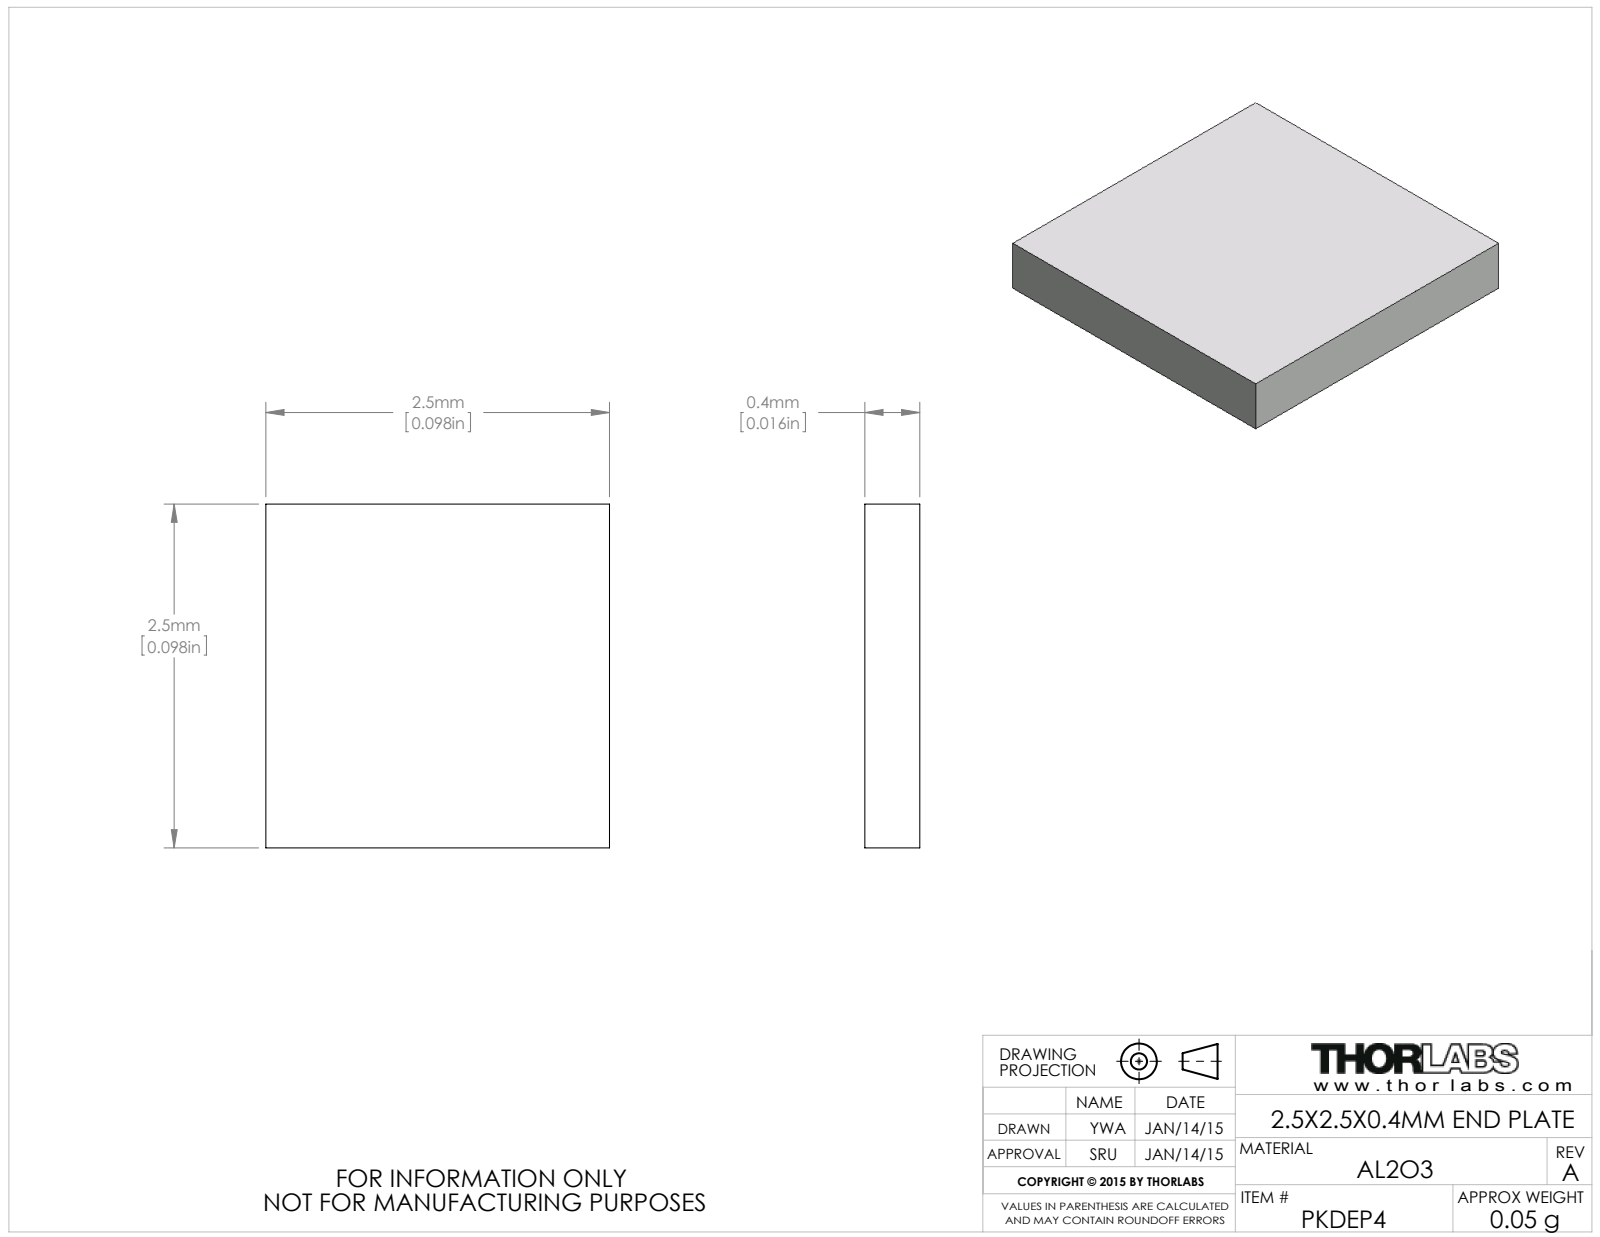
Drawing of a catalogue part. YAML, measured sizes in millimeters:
part_name: "PKDEP4"
step_written_by: "SolidWorks 2012 (AUTOMOTIVE_DESIGN)"
units: millimeters
bodies: {solids: 1, faces: 6, planar: 6, cylindrical: 0, other: 0}
overall_size: [2.5, 2.5, 0.4]
volume: 2
surface_area: 16
face_to_face_distances: [0.4, 2.5]
